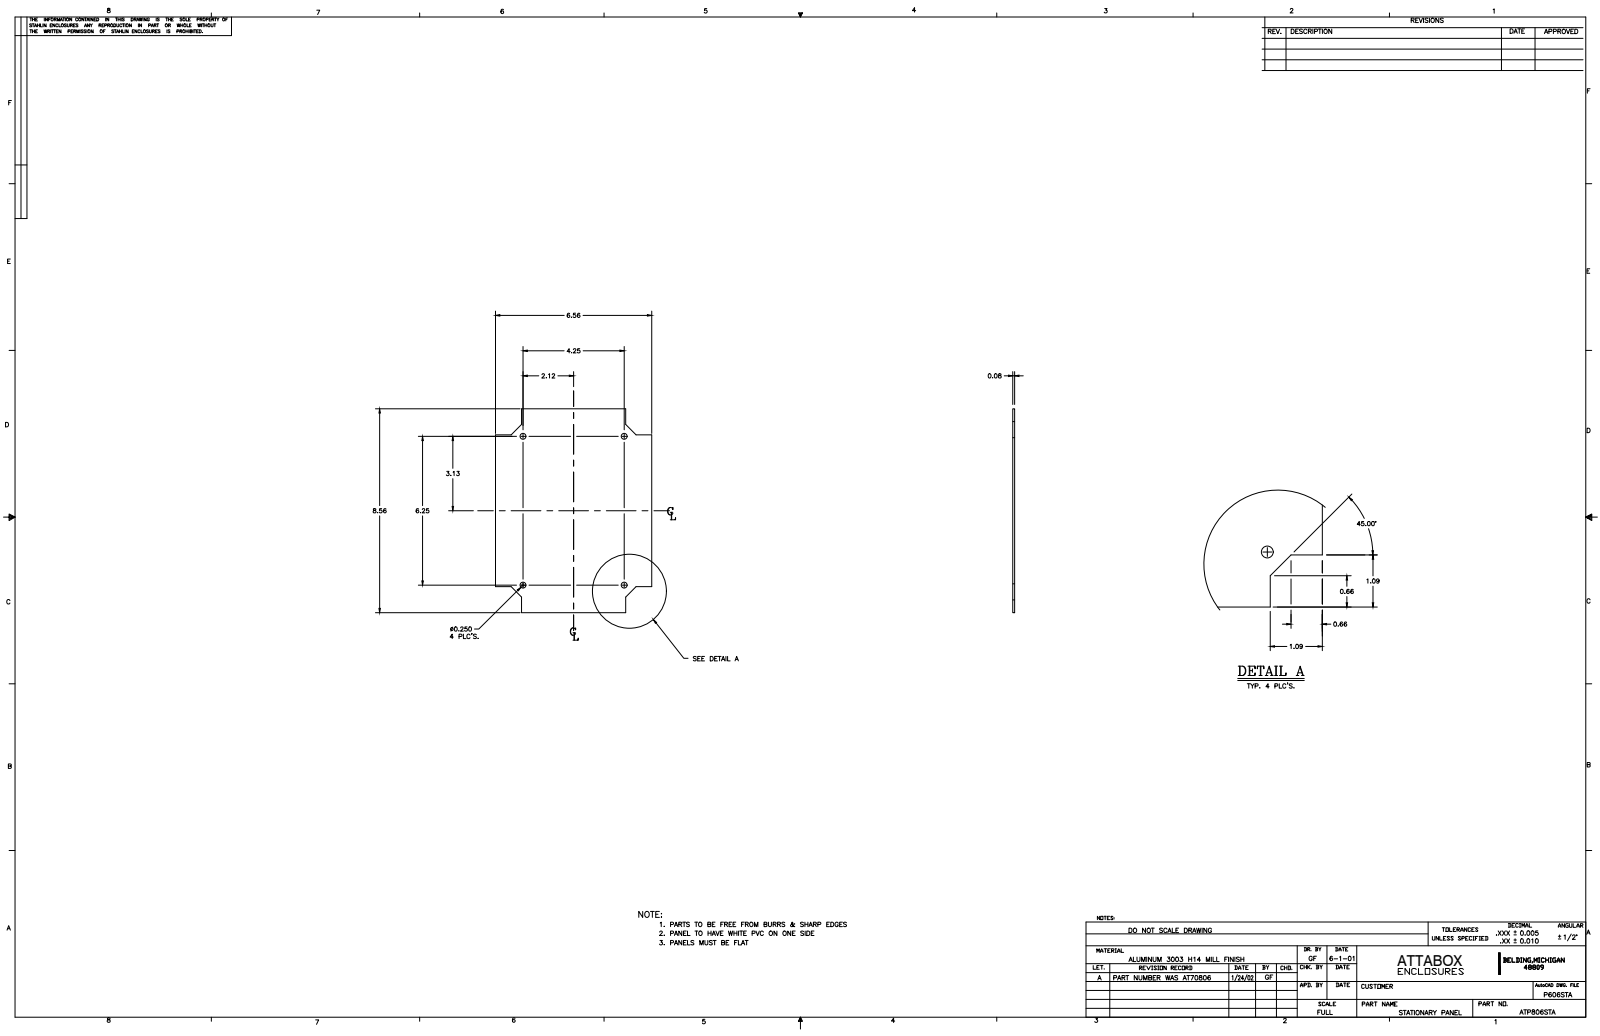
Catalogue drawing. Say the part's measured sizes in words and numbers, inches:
The part is named "P806STAL". Its 3-D file was written by "Autodesk Inventor 11 (AUTOMOTIVE_DESIGN)". It is 1 solid with 22 faces: 18 planar, 4 cylindrical and 0 other. Overall it measures 8.563 by 6.563 by 0.08 inches. Its volume is 4.127 cubic inches and its surface area 105.8 square inches. Round holes: 4 of diameter 0.25. The main face-to-face distances are 0.08, 6.562, 1.094, 8.562, 5.468, 7.468, 4.374, 6.374, 8.217. The hole center spacings are 4.25, 6.25, 7.558, 7.558.
